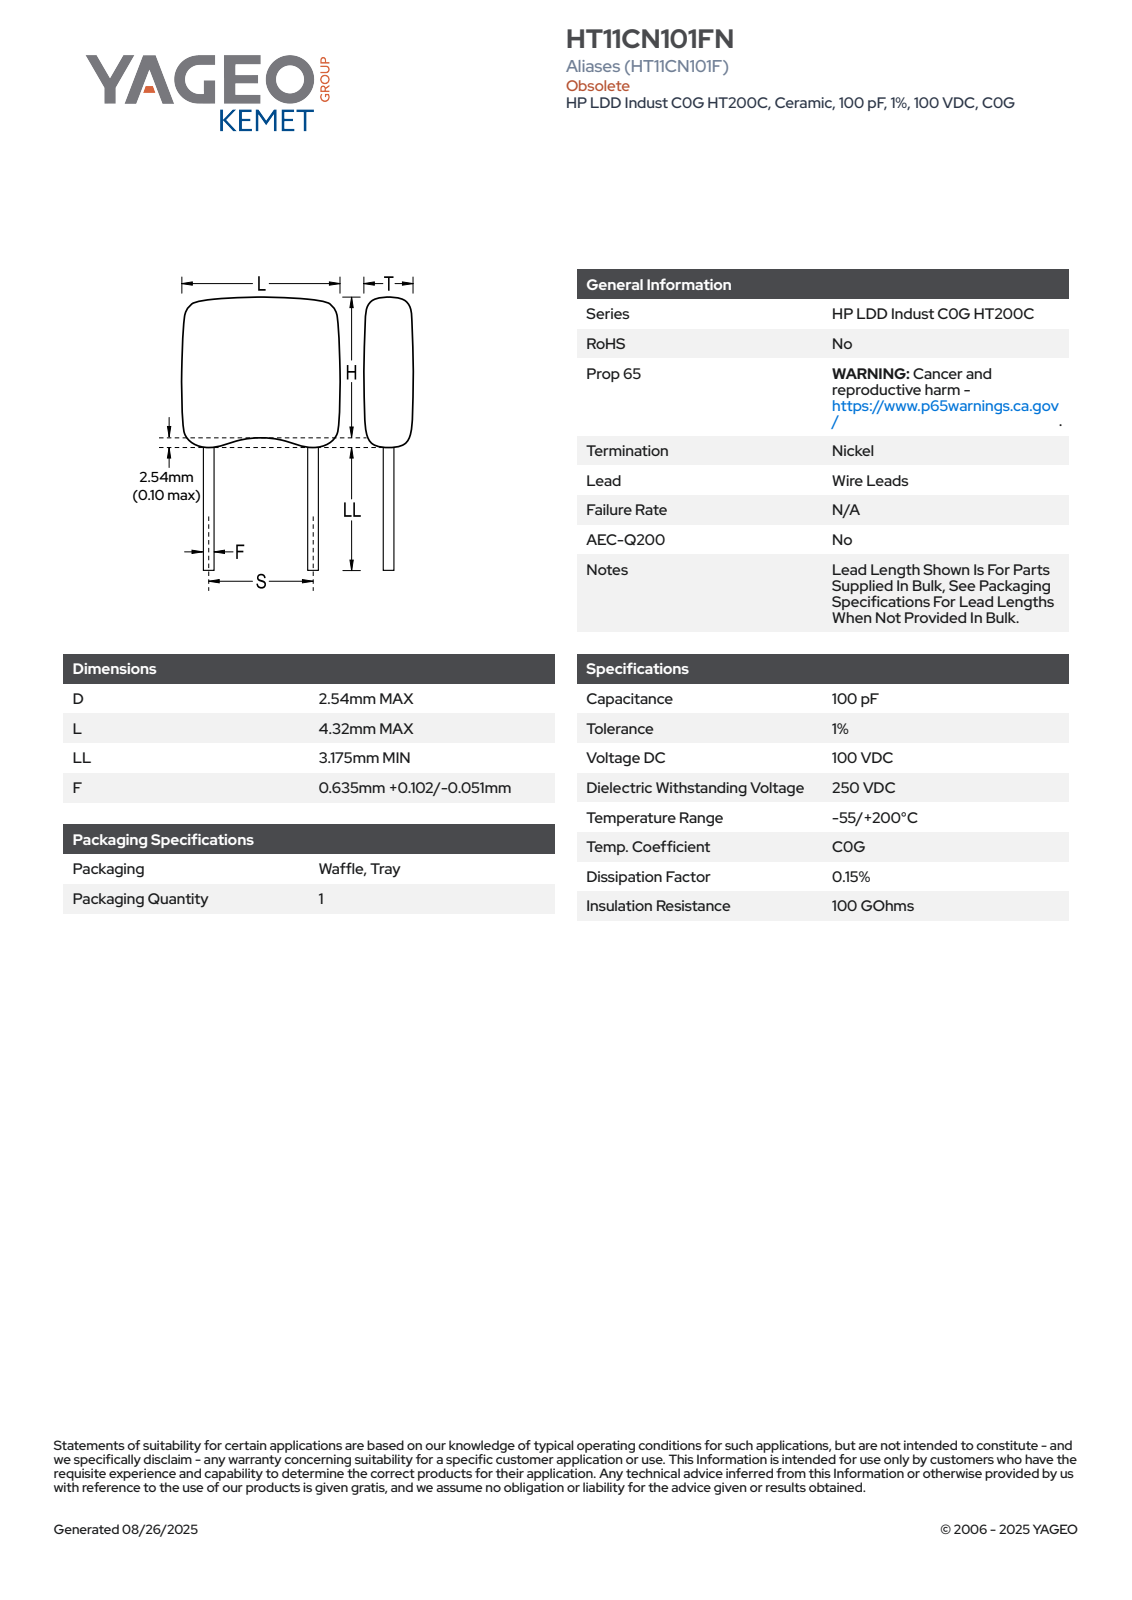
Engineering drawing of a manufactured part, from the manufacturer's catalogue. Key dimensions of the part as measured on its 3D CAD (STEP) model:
Part name (STEP PRODUCT): CCA_AMST_HT11_D2.54L4.32LL31.75F0.635
STEP written by: SolidWorks 2014 (AUTOMOTIVE_DESIGN)
Units: millimetres
Bodies: 1 solid, 67 faces (26 planar, 10 cylindrical, 31 other)
Overall size (bounding box): 67.82 × 2.56 × 2.55
Volume: 42 mm³ · Surface area: 172 mm²
Round bosses / shafts (diameter × count): ⌀2.54 ×1, ⌀0.64 ×1
Partial cylindrical surfaces — rounded edges, fillets, slot ends (radius × count): R1.28 ×1
Main face-to-face distances: 4.32, 31.75, 36.07, 67.82, 32.64, 0.89, 3.43, 35.18, 33.45, 1.7
